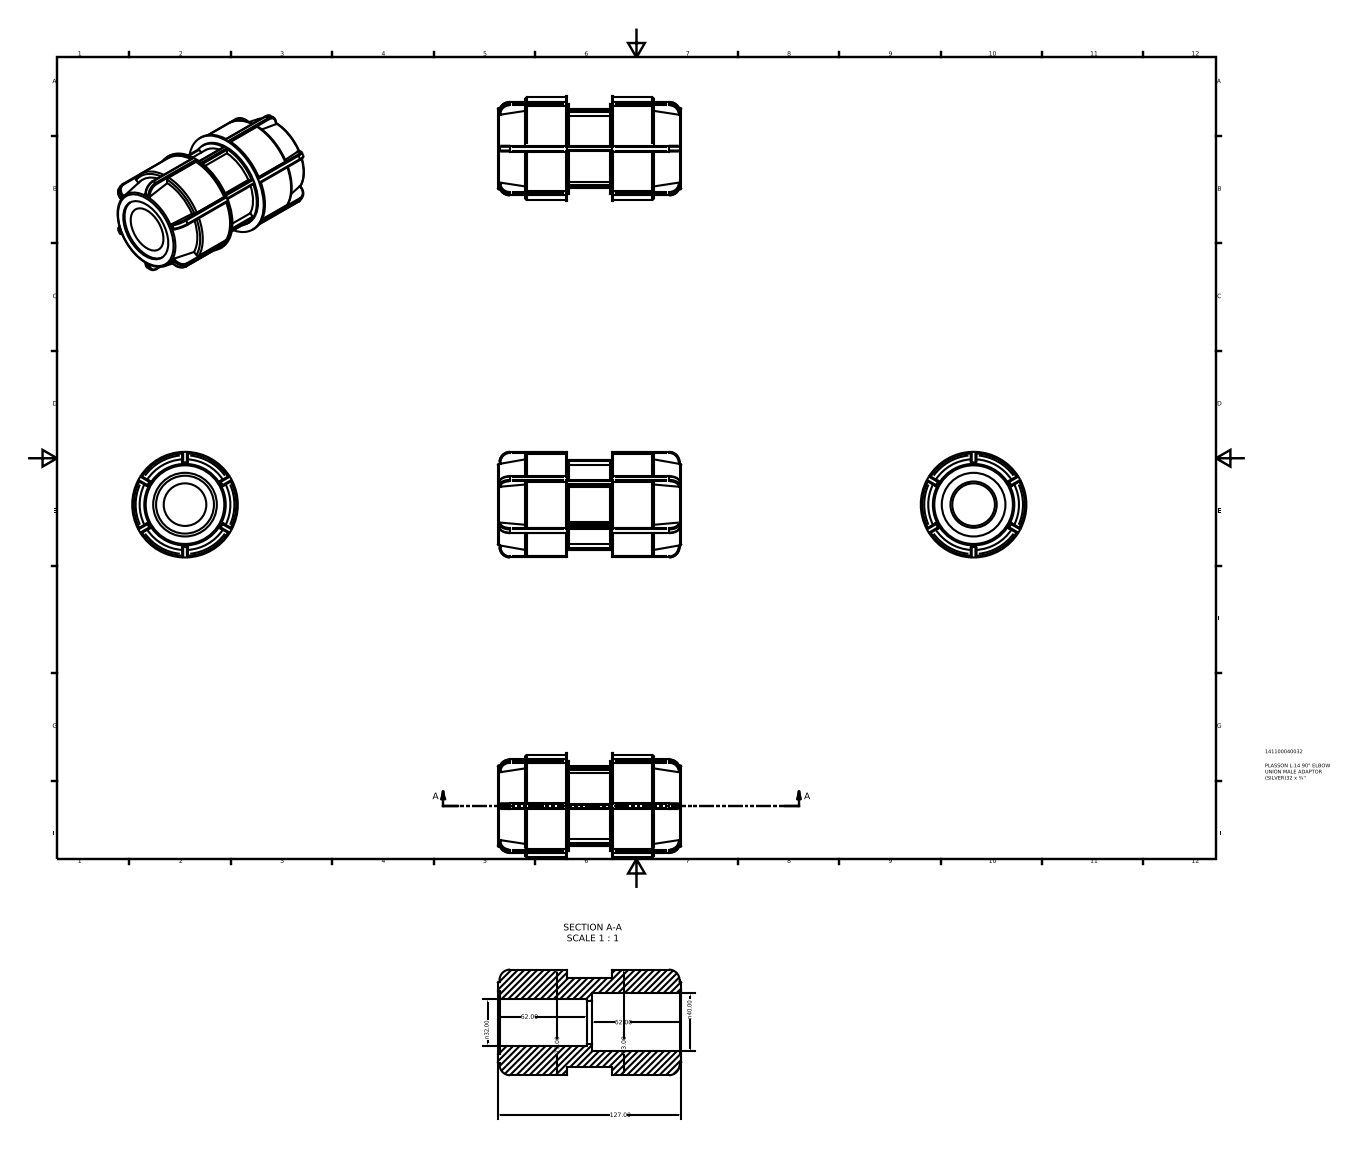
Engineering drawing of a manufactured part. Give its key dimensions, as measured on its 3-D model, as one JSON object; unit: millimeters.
{"part_name": "141100040032", "step_written_by": "Autodesk Inventor 2015 (AUTOMOTIVE_DESIGN)", "units": "millimeters", "bodies": {"solids": 1, "faces": 230, "planar": 92, "cylindrical": 86, "other": 52}, "overall_size": [127, 73, 73], "volume_mm3": 287170, "surface_area_mm2": 52949, "round_holes": [[29.44, 1], [32, 1], [40, 1], [44, 1]], "round_bosses_or_shafts": [[73, 1], [70.81, 1], [62.05, 1], [54.75, 1]], "partial_cylinders_radius": [[0.73, 44]], "face_to_face_distances": [1.27, 30.48, 48.26, 77.47, 29.21, 78.74, 46.99, 4, 49.53, 27.94]}
